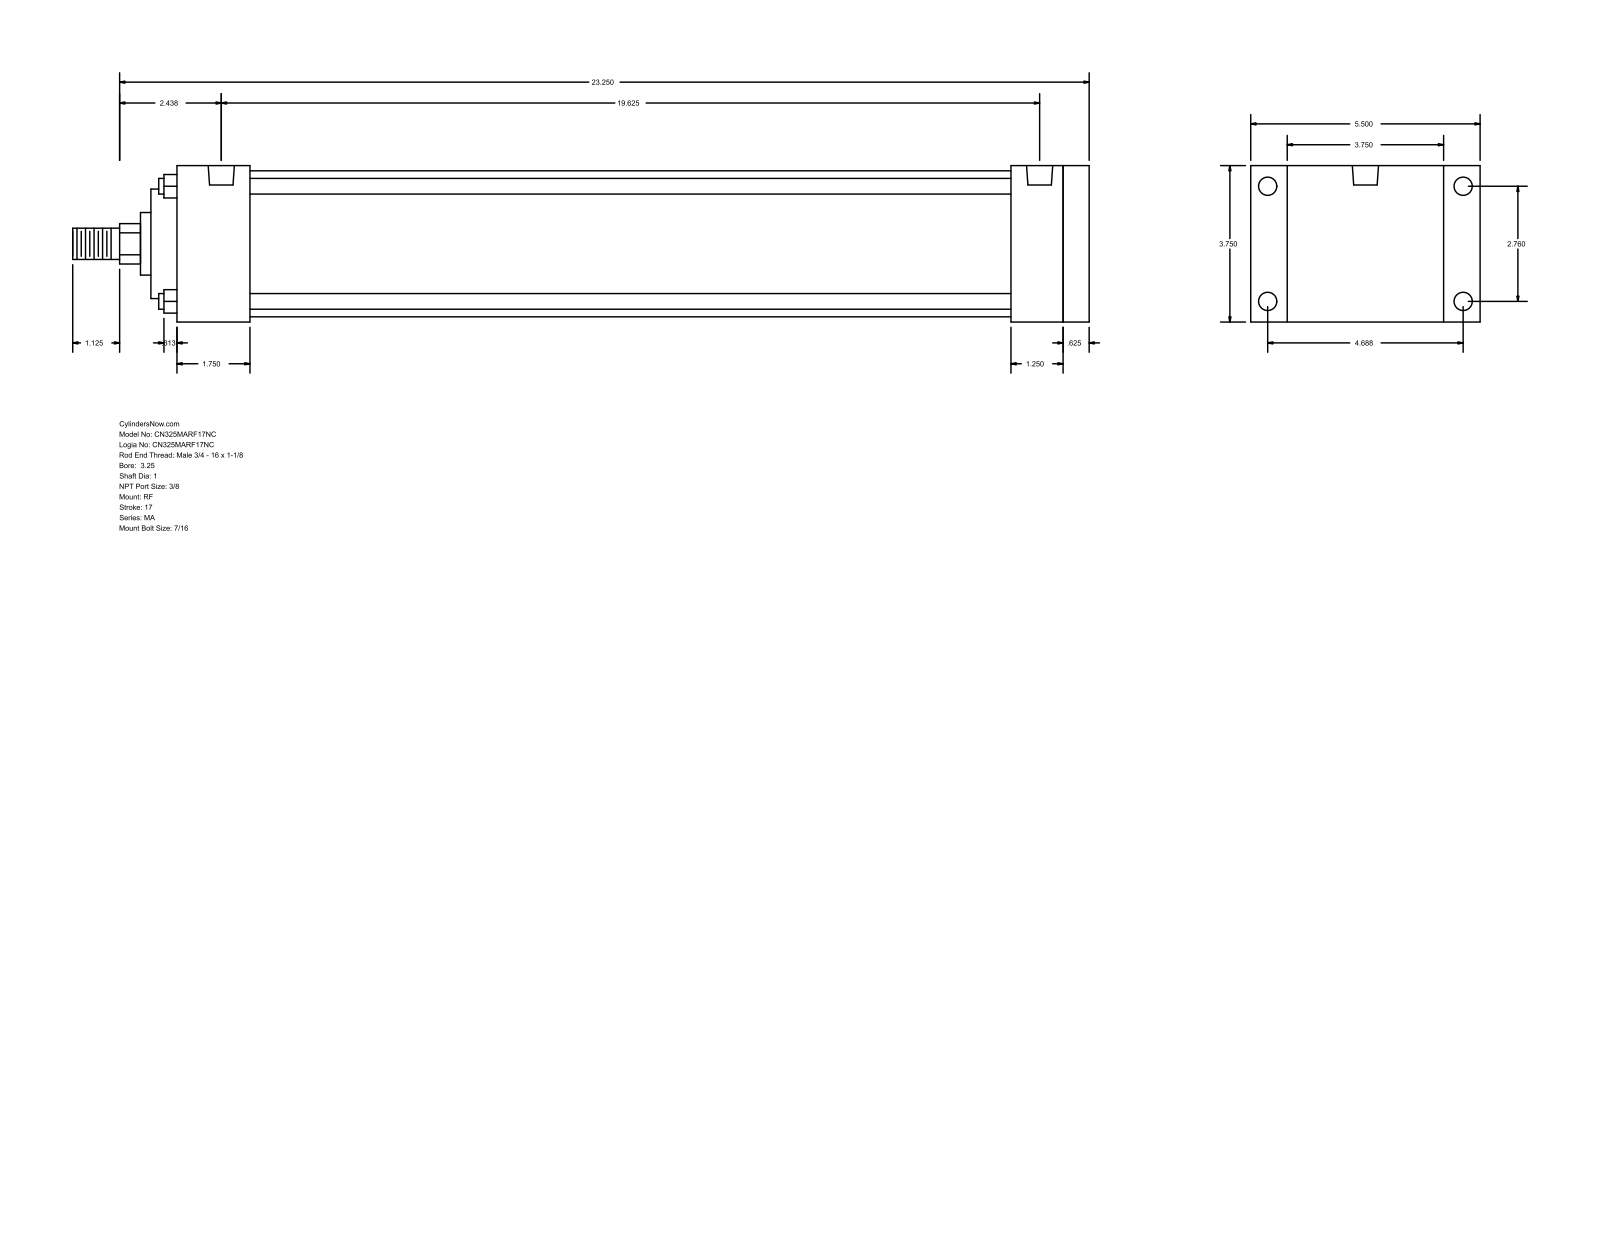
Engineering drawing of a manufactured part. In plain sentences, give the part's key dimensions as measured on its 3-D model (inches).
The part is named "MA_RF__0325_1". Its 3-D file was written by "GSSL Pune (CONFIG_CONTROL_DESIGN)". It is 0 solids with 94 faces: 65 planar, 29 cylindrical and 0 other. Overall it measures 24.375 by 5.5 by 3.75 inches. Round holes: 8 of diameter 0.437, 2 of diameter 0.627. Round bosses or shafts: 4 of diameter 0.375, 1 of diameter 3.5, 1 of diameter 2.625, 1 of diameter 1.5, 1 of diameter 1, 1 of diameter 0.75. Partial cylindrical surfaces (rounded edges, fillets, slot ends): 1 of radius 0.484. The main face-to-face distances are 3.75, 21.875, 21.25, 0.625, 0.875, 4.625, 20, 1.25, 1.875, 1.75. The hole center spacings are 2.76, 4.687, 5.439, 19.25, 0.187, 0.188, 19.437, 19.438.
